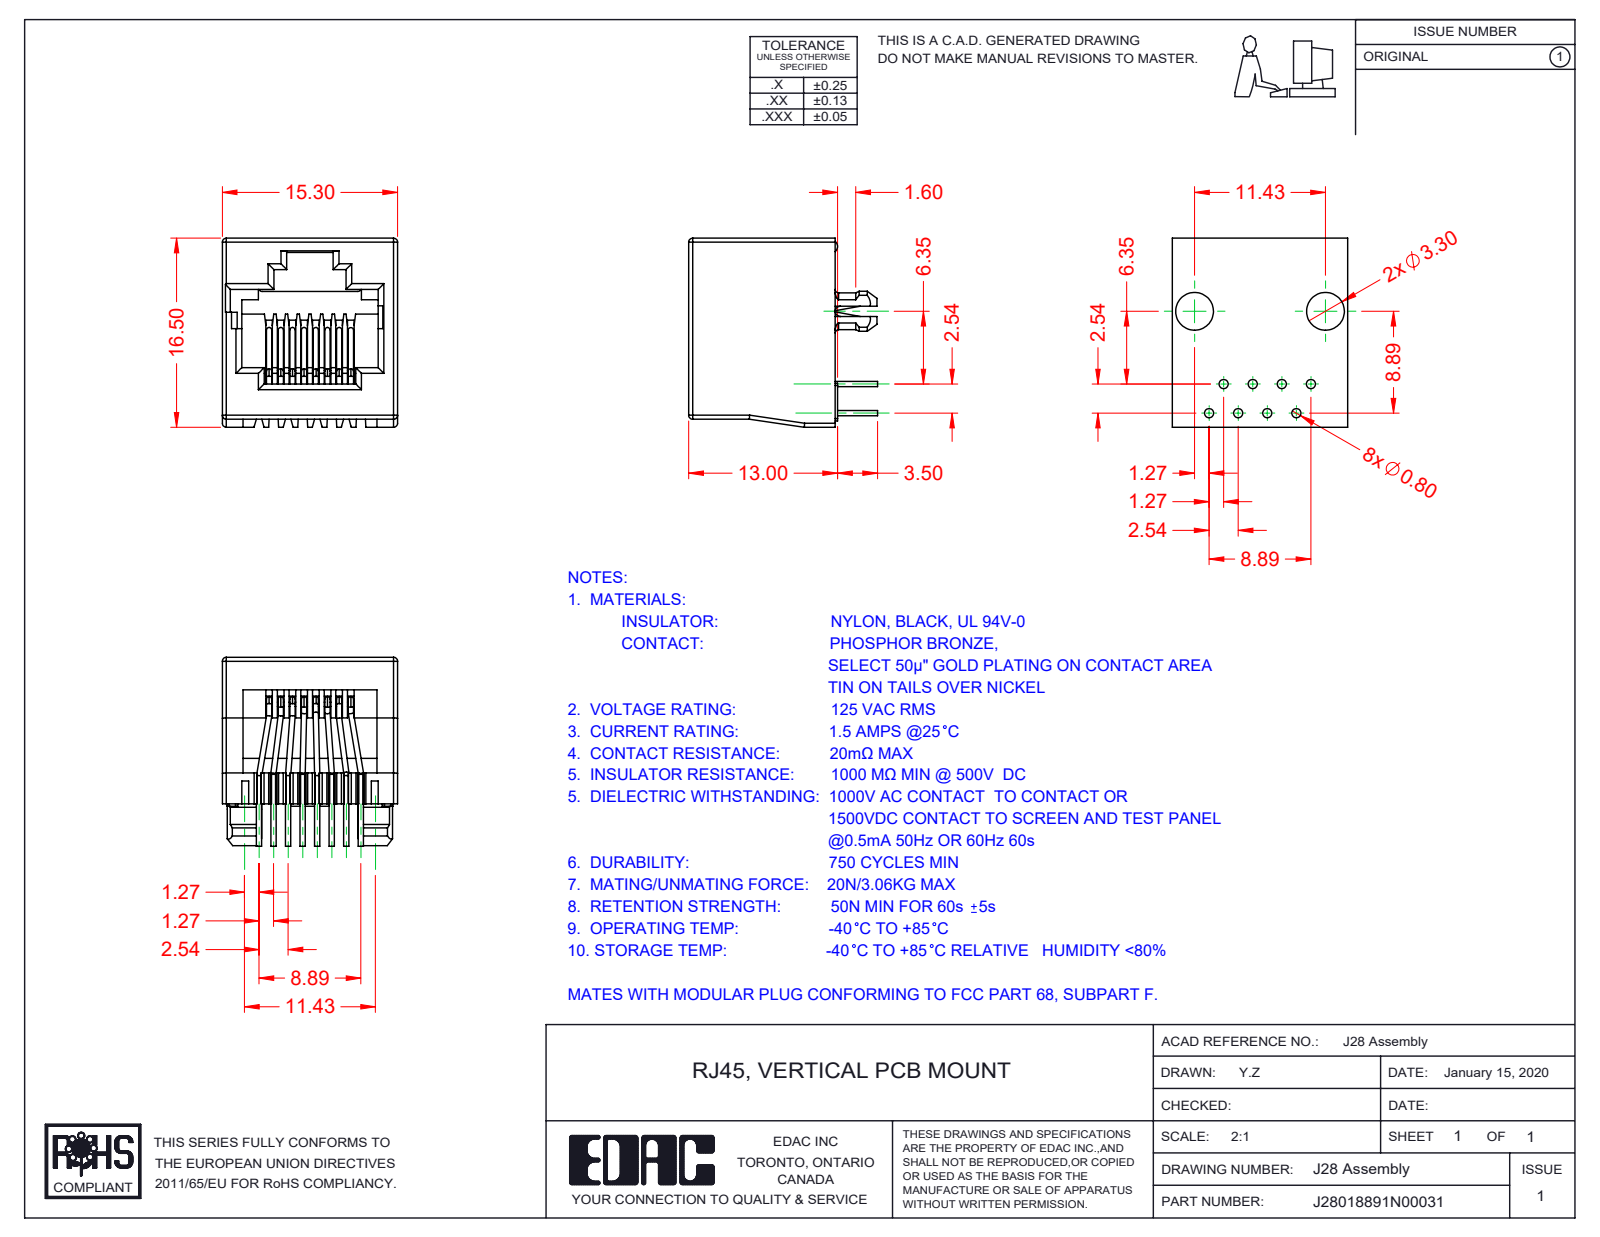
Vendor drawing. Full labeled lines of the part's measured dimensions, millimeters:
Part name (STEP PRODUCT): RJ28018891N00031; 28 Contacts; 28 Insulator
STEP written by: SolidWorks 2016 (CONFIG_CONTROL_DESIGN)
Units: millimetres
Bodies: 9 solids, 580 faces (319 planar, 205 cylindrical, 56 other)
Overall size (bounding box): 16.5 × 16.5 × 15.3
Volume: 1 535 mm³ · Surface area: 2 745 mm²
Round holes (diameter × count): ⌀1.6 ×2
Round bosses / shafts (diameter × count): ⌀0.46 ×45
Partial cylindrical surfaces — rounded edges, fillets, slot ends (radius × count): R0.5 ×19, R0.1 ×16, R0.35 ×14, R0.25 ×10, R0.2 ×8, R0.23 ×8, R0.45 ×2, R1.6 ×2
Main face-to-face distances: 15.3, 1.02, 1.7, 13.6, 1.25, 2.04, 12.81, 3.06, 3.15, 12.15
Hole centre spacings: 12
